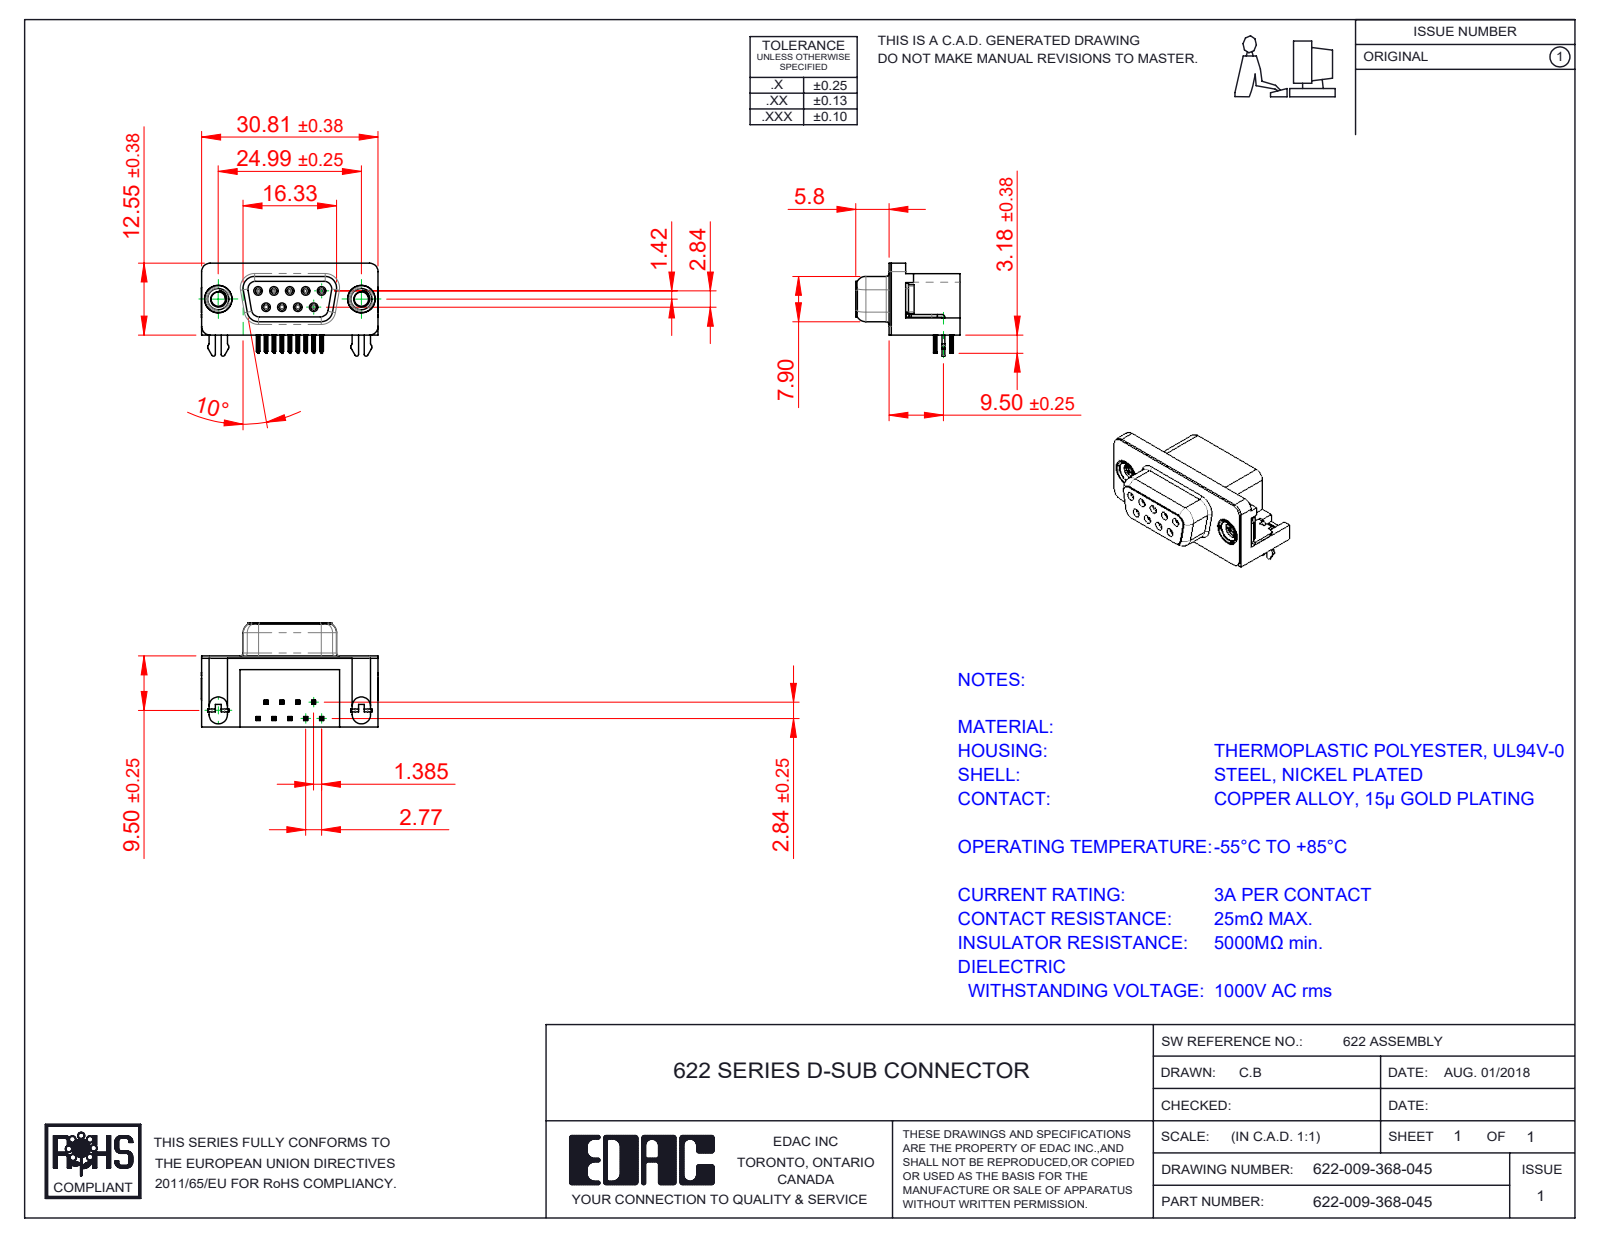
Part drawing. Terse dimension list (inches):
name: 622 Contact Top; 622 Housing_9 Socket; 622 Shell_9 Socket; 622 Socket Bottom (+3 more)
written by: SolidWorks 2016 (CONFIG_CONTROL_DESIGN)
unit: in
bodies: 15 solids, 1692 faces (726 planar, 426 cylindrical, 540 other)
size: 1.216 × 0.717 × 0.64
volume: 0.228 in³; area: 7.984 in²
holes: 9× ⌀0.031, 9× ⌀0.035, 2× ⌀0.079, 2× ⌀0.098, 2× ⌀0.157, 2× ⌀0.189, 2× ⌀0.197
bosses: 9× ⌀0.047, 2× ⌀0.193, 2× ⌀0.187, 2× ⌀0.154, 2× ⌀0.118
rounds: 72× R0.004, 36× R0.006, 18× R0.014, 18× R0.039, 12× R0.01, 9× R0.013, 8× R0.053, 8× R0.063
face distances: 0.016, 0.472, 0.488, 0.014, 0.114, 0.098, 0.244, 0.407, 0.374, 0.228
hole spacings: 0.124, 0.109, 0.218, 0.198, 0.198, 0.327, 0.294, 0.295
